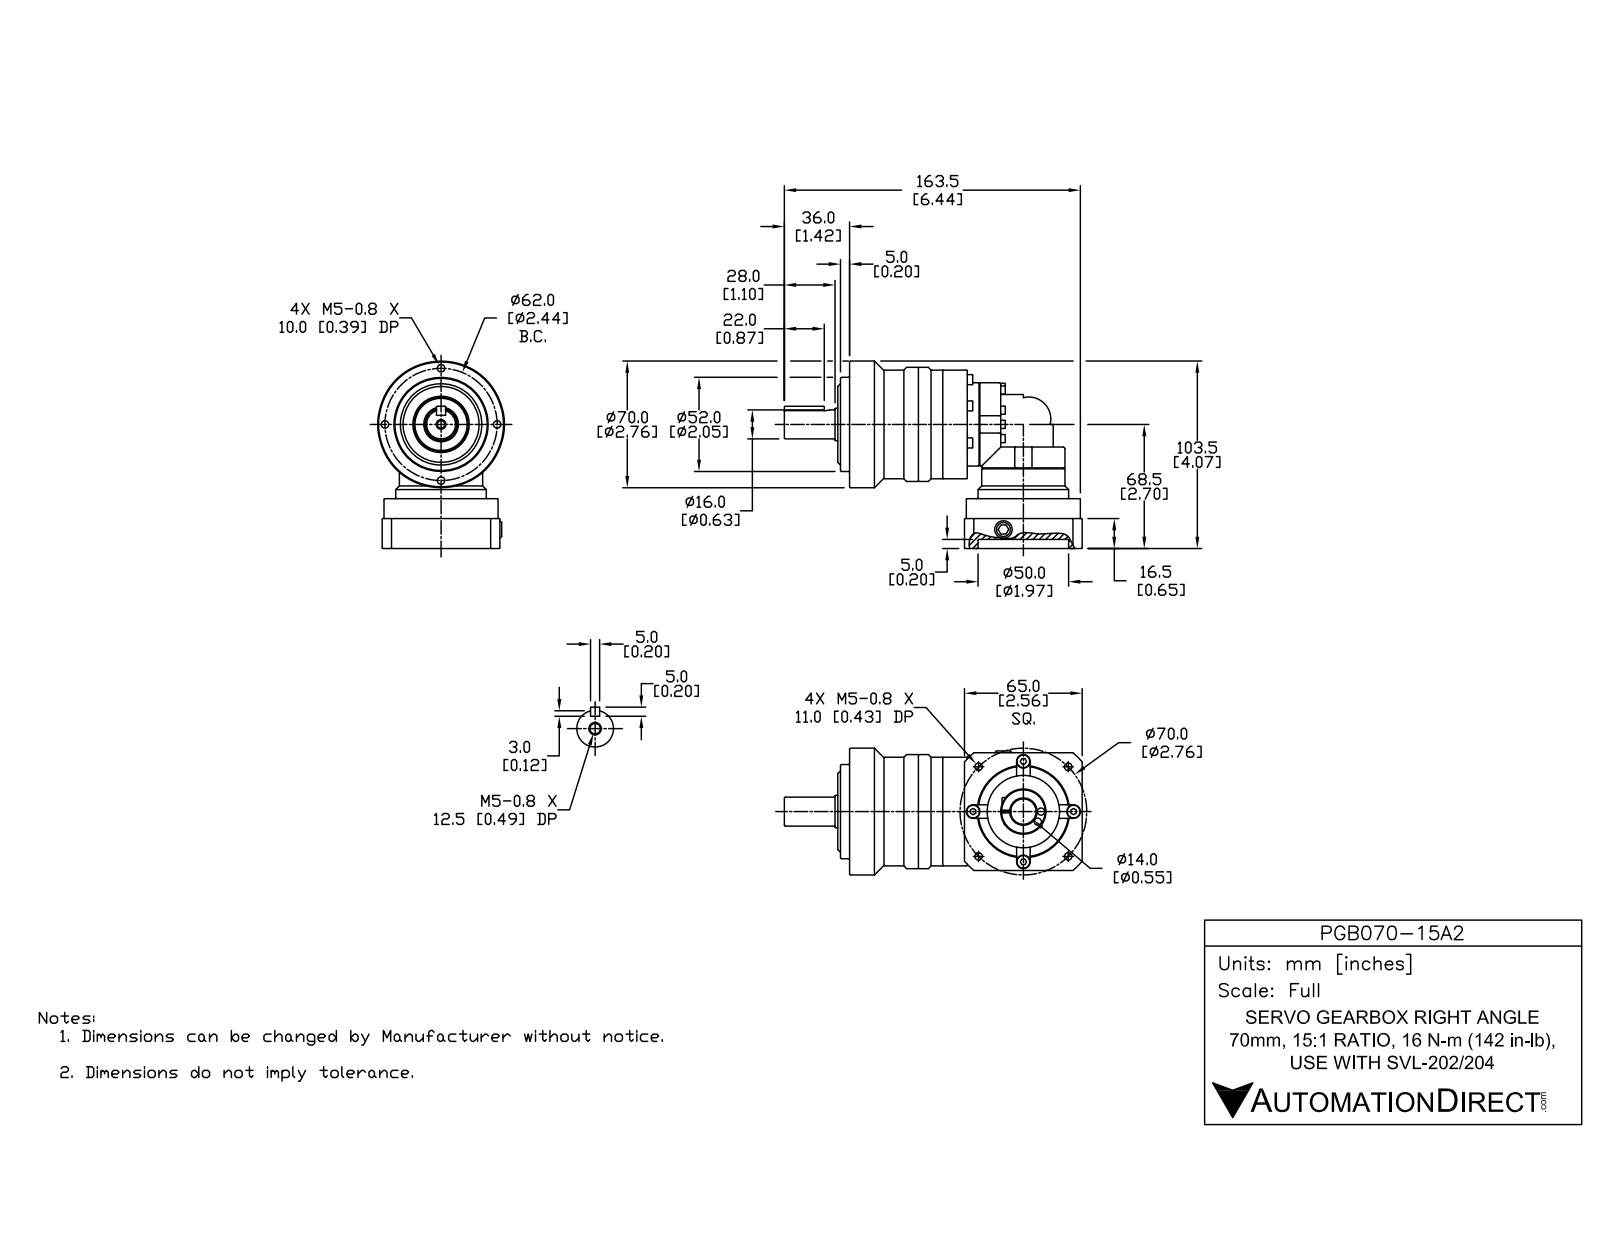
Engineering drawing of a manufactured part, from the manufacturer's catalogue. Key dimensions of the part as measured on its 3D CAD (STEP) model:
Part name (STEP PRODUCT): PGB070-15A2
STEP written by: SolidWorks 2014 (AUTOMOTIVE_DESIGN)
Units: inches
Bodies: 1 solid, 690 faces (286 planar, 184 cylindrical, 220 other)
Overall size (bounding box): 6.476 × 4.075 × 2.756
Volume: 24.19 in³ · Surface area: 82.74 in²
Round holes (diameter × count): ⌀0.163 ×9, ⌀0.128 ×8, ⌀0.138 ×7, ⌀0.295 ×4, ⌀0.157 ×2, ⌀0.097 ×1, ⌀0.315 ×1, ⌀0.551 ×1, ⌀1.575 ×1, ⌀1.969 ×1
Round bosses / shafts (diameter × count): ⌀0.177 ×9, ⌀0.217 ×7, ⌀0.118 ×7, ⌀0.276 ×4, ⌀2.48 ×2, ⌀1.811 ×2, ⌀1.772 ×2, ⌀2.756 ×1
Partial cylindrical surfaces — rounded edges, fillets, slot ends (radius × count): R0.039 ×6, R0.65 ×2, R0.098 ×1, R0.128 ×1, R1.673 ×1
Main face-to-face distances: 2.559, 0.65, 2.5, 0.059, 2.756, 0.197, 1.083, 0.256, 0.433, 2.815
Hole centre spacings: 0.836, 0.981, 1.093, 1.545, 1.759, 2.019, 2.285, 0.473
